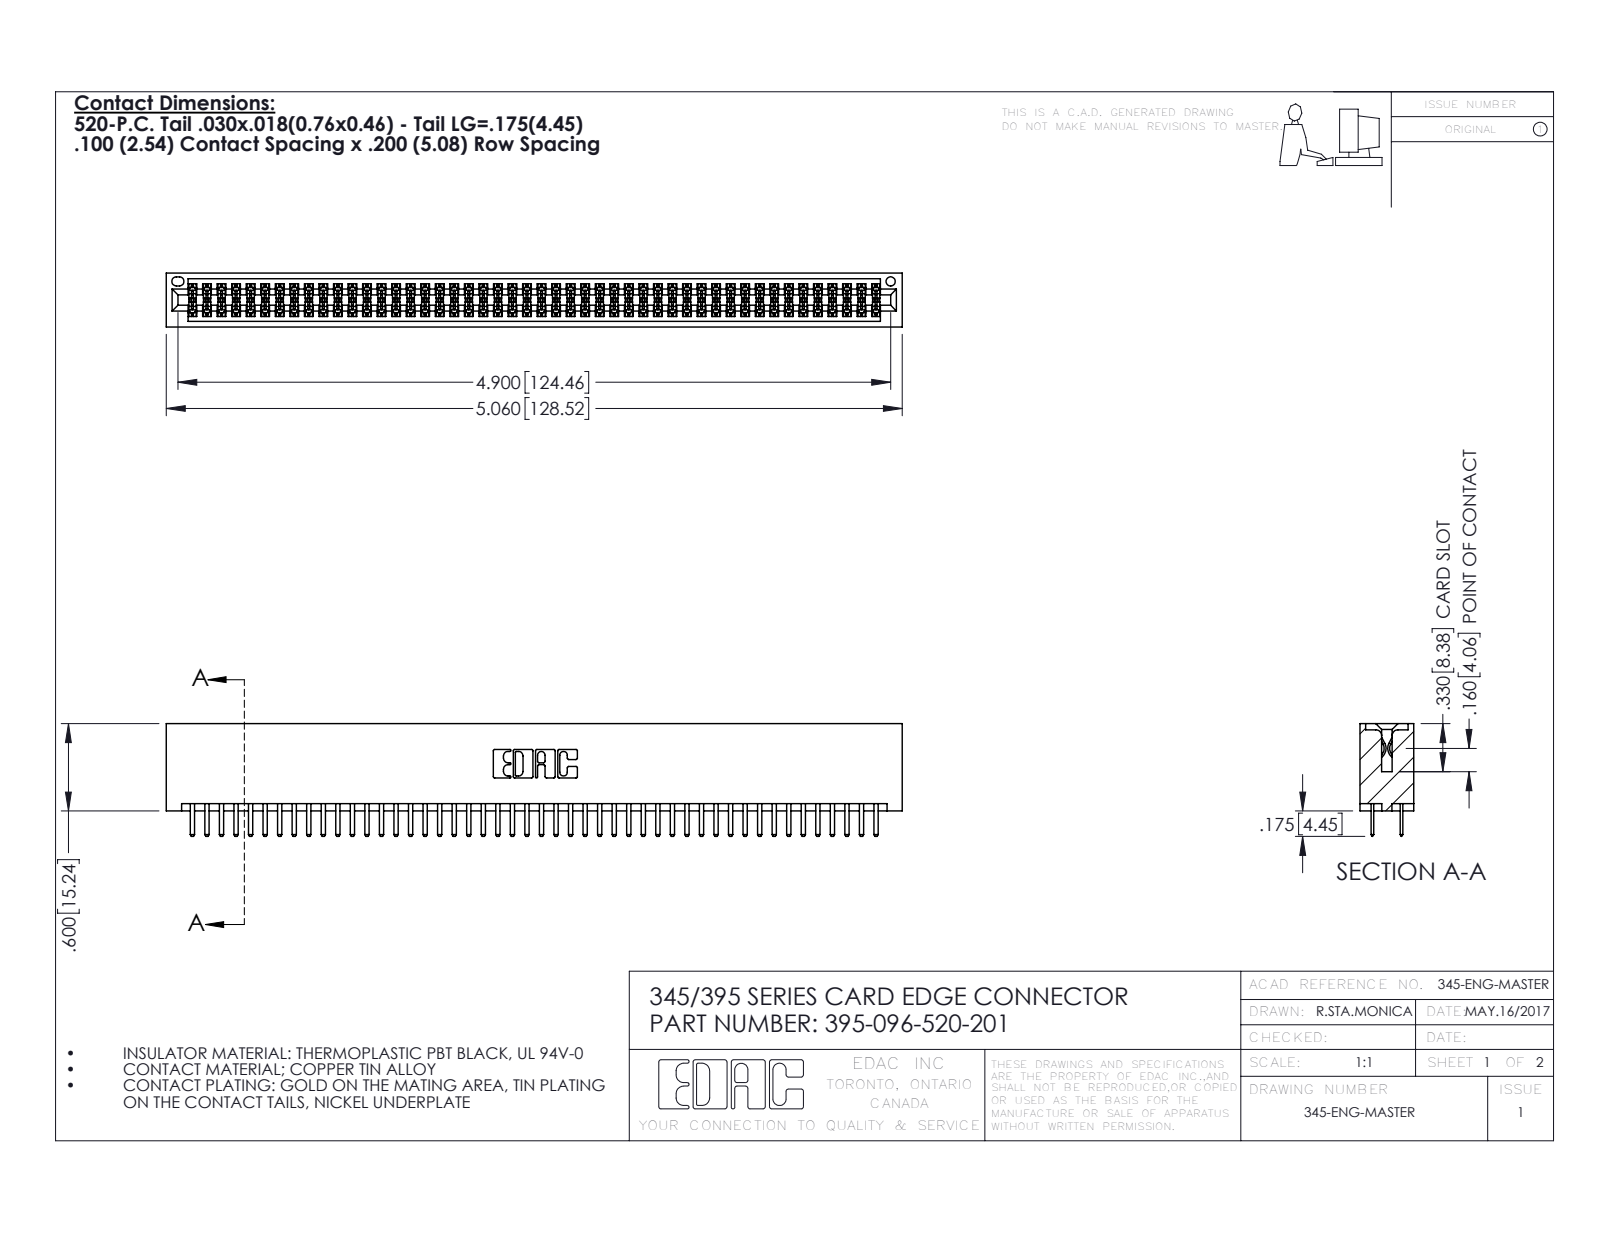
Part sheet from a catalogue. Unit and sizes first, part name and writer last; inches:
Units: inches
Overall size (bounding box): 5.06 × 0.775 × 0.37
Round holes (diameter × count): ⌀0.064 ×1
Partial cylindrical surfaces — rounded edges, fillets, slot ends (radius × count): R0.006 ×144, R0.01 ×100, R0.01 ×22, R0.007 ×6, R0.031 ×6, R0.026 ×3, R0.014 ×2, R0.019 ×2
Main face-to-face distances: 0.298, 0.072, 0.2, 0.37, 0.098, 0.272, 0.025, 0.225, 0.022, 0.072
Volume: 0.8 in³ · Surface area: 30.56 in²
Bodies: 97 solids, 5302 faces (3436 planar, 1866 cylindrical, 0 other)
Part name (STEP PRODUCT): 345 Part_No Mounting Lugs; 395-096-520-201; 345-292-001_345-293-120
STEP written by: SolidWorks 2016 (CONFIG_CONTROL_DESIGN)
